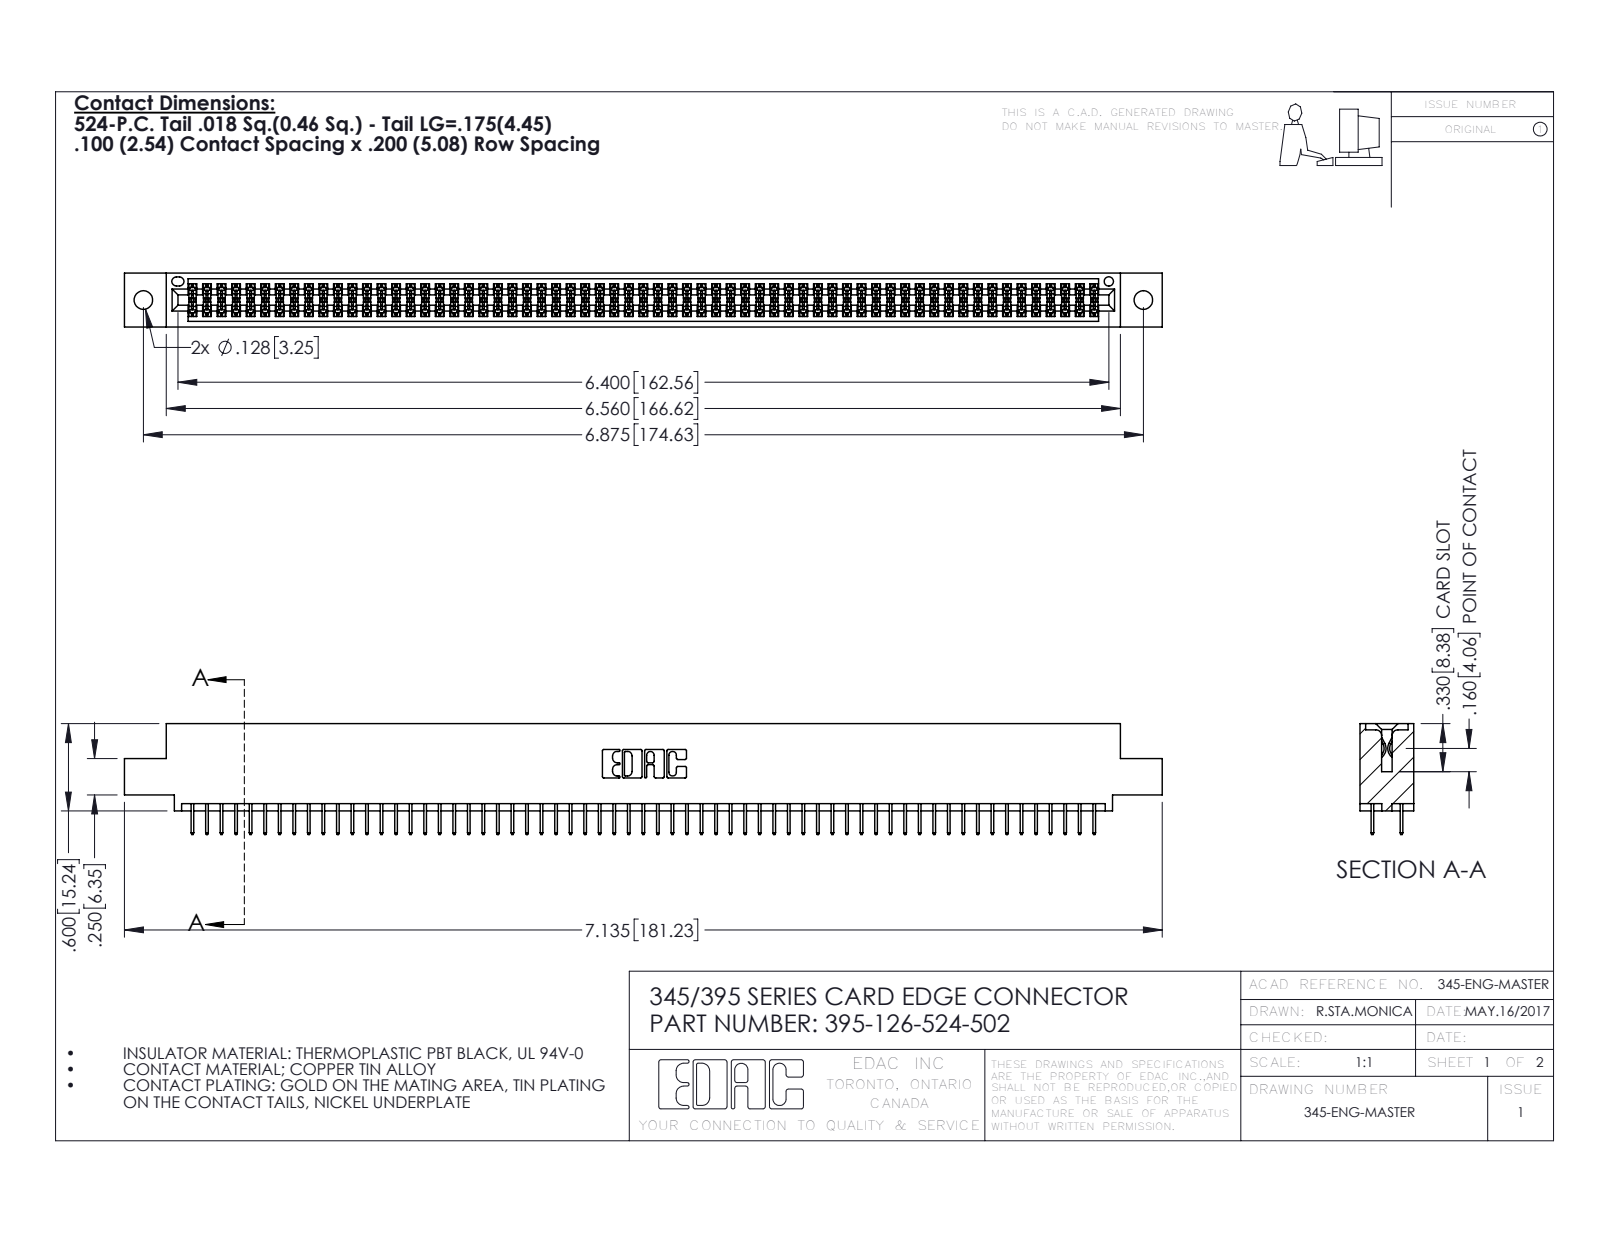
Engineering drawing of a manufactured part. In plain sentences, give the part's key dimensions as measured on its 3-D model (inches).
The part is named "395-126-524-502; 345-292-001_345-293-124; 345 Part_0.110 Offset - 0.128 Dia". Its 3-D file was written by "SolidWorks 2016 (CONFIG_CONTROL_DESIGN)". It is 127 solids with 6934 faces: 4998 planar, 1936 cylindrical and 0 other. Overall it measures 7.135 by 0.762 by 0.37 inches. Its volume is 1.068 cubic inches and its surface area 39.66 square inches. Round holes: 2 of diameter 0.128, 1 of diameter 0.064. Partial cylindrical surfaces (rounded edges, fillets, slot ends): 189 of radius 0.006, 22 of radius 0.01, 6 of radius 0.007, 6 of radius 0.031, 3 of radius 0.026, 2 of radius 0.014, 2 of radius 0.019, 2 of radius 0.022. The main face-to-face distances are 0.072, 0.298, 0.2, 0.37, 0.098, 0.272, 0.025, 0.225, 0.072, 0.175. The hole center spacings are 0.27, 6.639, 6.875.
